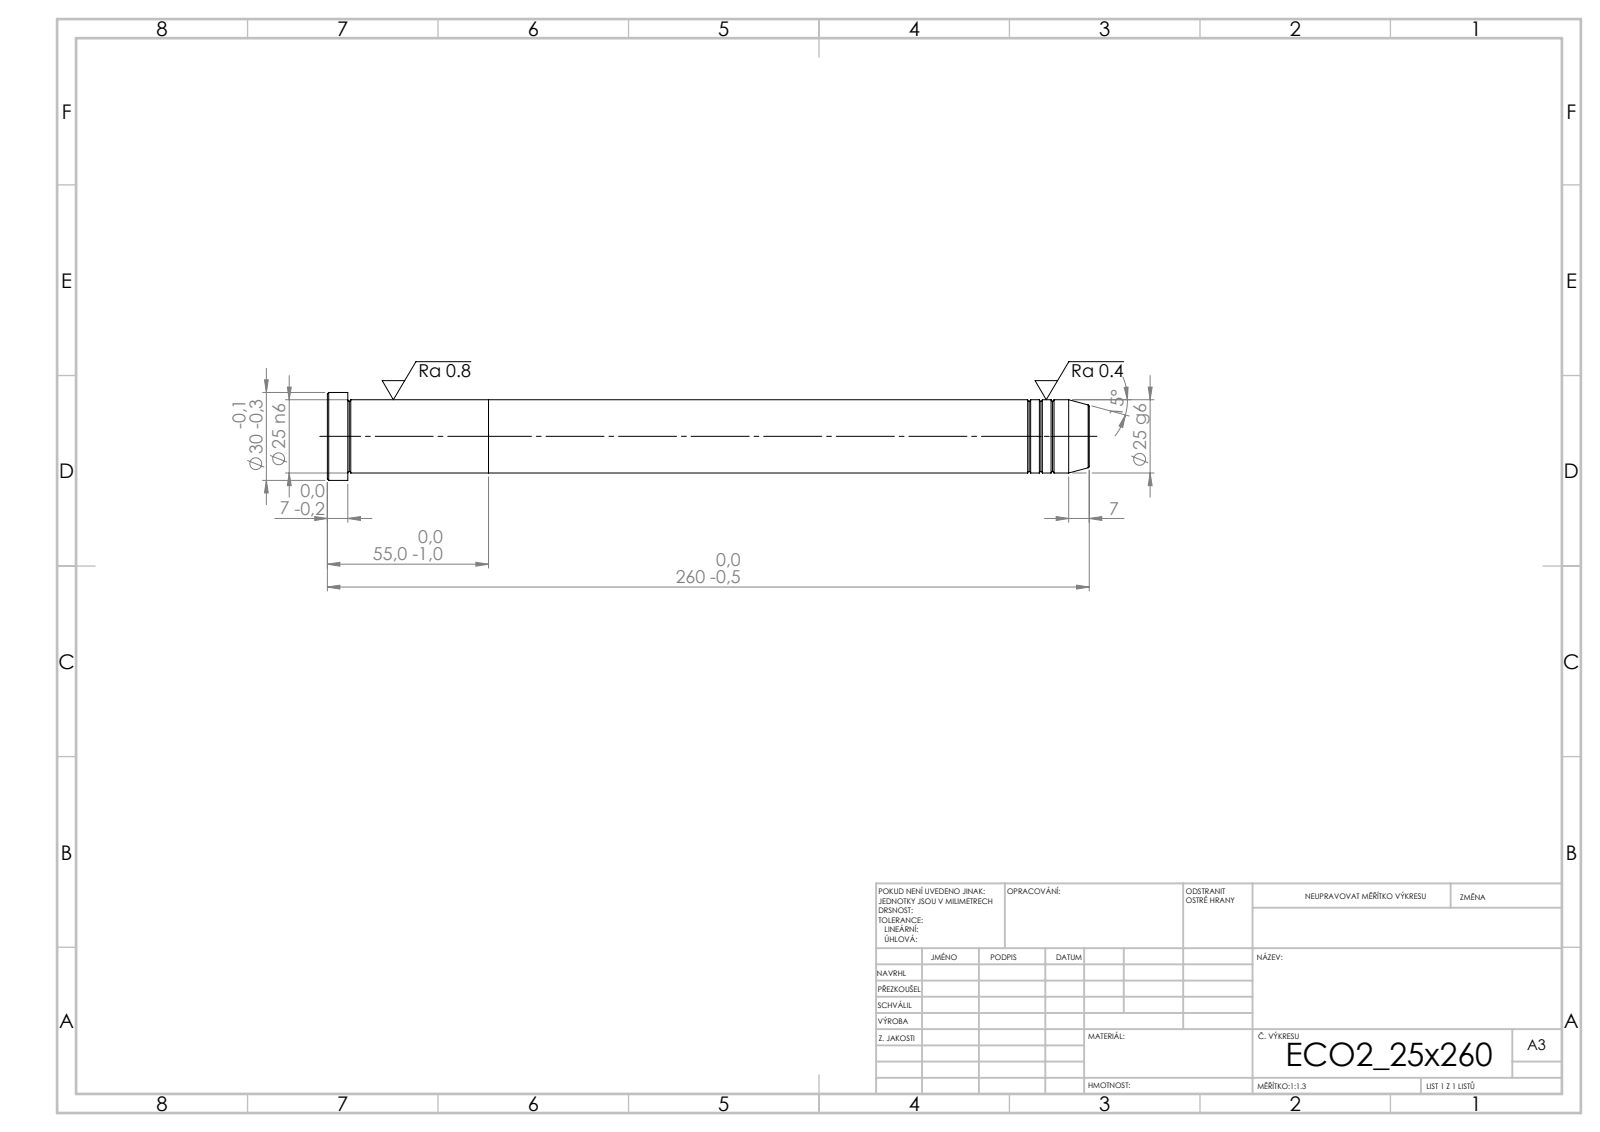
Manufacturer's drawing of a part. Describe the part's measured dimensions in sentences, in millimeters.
Its 3-D file was written by "SolidWorks 2019 (CONFIG_CONTROL_DESIGN)". It is 2 solids with 39 faces: 5 planar, 12 cylindrical and 22 other. Overall it measures 260 by 30 by 30 millimeters. Its volume is 128 514 cubic millimeters and its surface area 22 897 square millimeters. Round bosses or shafts: 1 of diameter 30, 1 of diameter 25. The main face-to-face distances are 55, 205, 260, 253, 48, 7.
